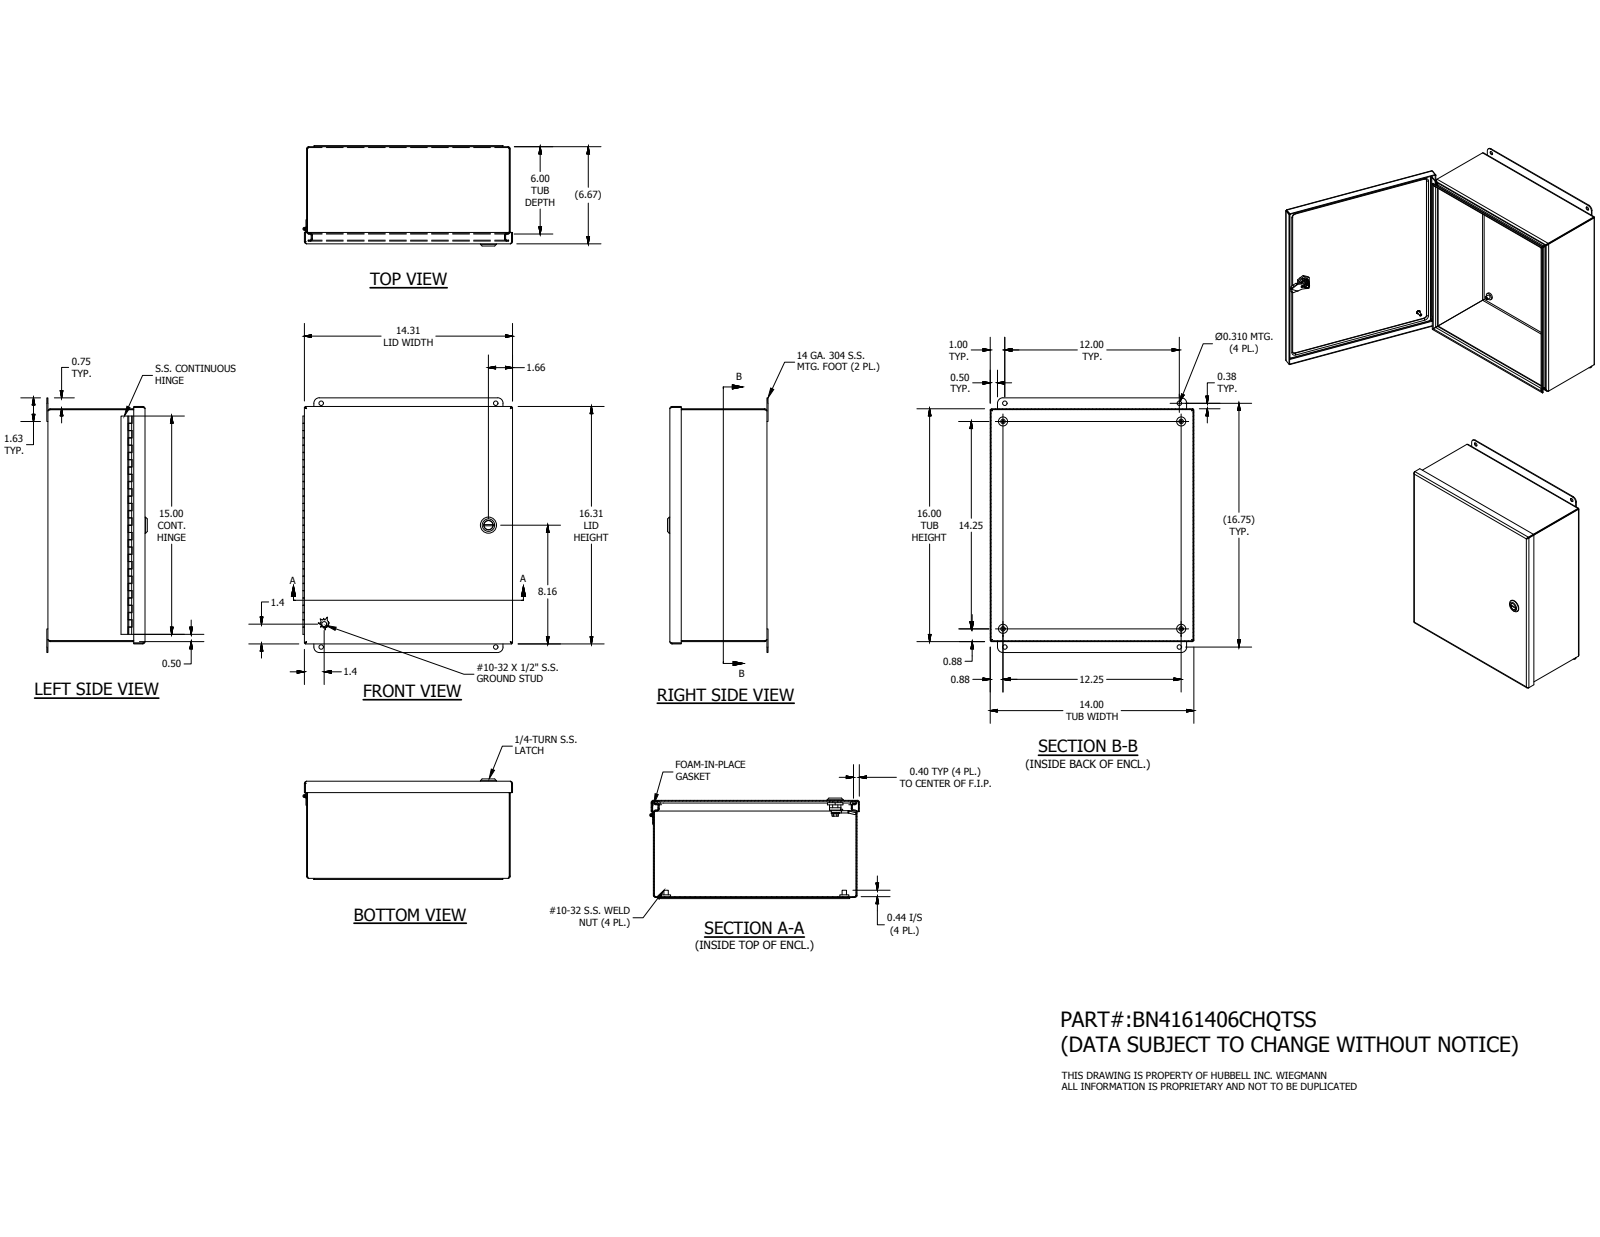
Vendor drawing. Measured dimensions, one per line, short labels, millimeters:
name: BN41614CHQTSSLID; 16x14; 34857; H4050555LH (+8 more)
written by: Autodesk Inventor 2016 (AUTOMOTIVE_DESIGN)
unit: mm
bodies: 19 solids, 668 faces (359 planar, 215 cylindrical, 94 other)
size: 444.5 × 366.06 × 175.39
volume: 1 041 000 mm³; area: 1 315 000 mm²
holes: 4× ⌀3.96, 4× ⌀7.87, 1× ⌀2.96, 1× ⌀5, 1× ⌀8, 1× ⌀10, 1× ⌀10.2, 1× ⌀16.1
bosses: 4× ⌀15.88, 4× ⌀7.62, 1× ⌀28, 1× ⌀19.8, 1× ⌀16, 1× ⌀15.2, 1× ⌀13.5, 1× ⌀12.8
rounds: 20× R2.38, 20× R3.88, 16× R3.17, 8× R0.5, 4× R4, 4× R9.53, 2× R2.31, 1× R6.45
face distances: 1.5, 1.49, 167.99, 169.48, 166.49, 167.98, 404.9, 352.61, 354.1, 354.11
hole spacings: 31.91, 393.71, 499.85, 304.8, 309.6, 309.61, 311.15, 346.32
